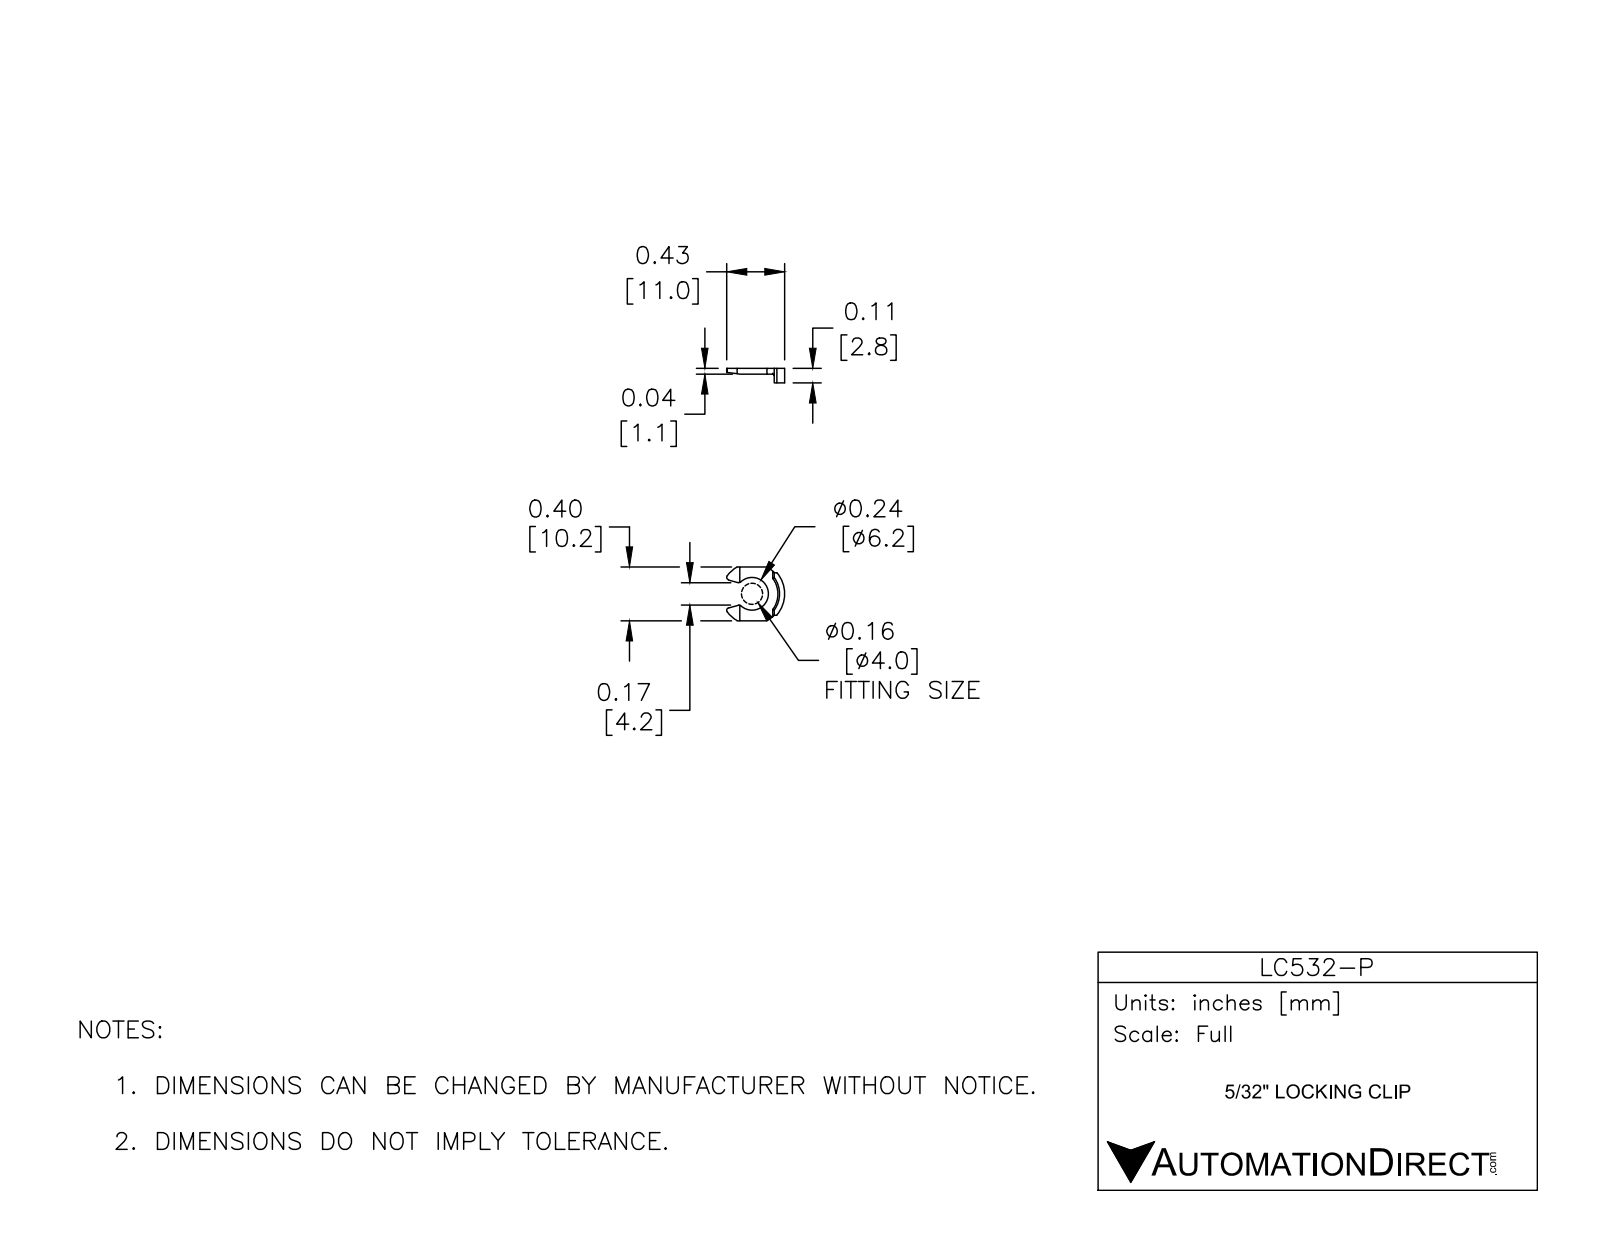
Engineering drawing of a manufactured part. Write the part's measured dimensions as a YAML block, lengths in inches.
part_name: "LC532-P"
step_written_by: "SolidWorks 2017 (AUTOMOTIVE_DESIGN)"
units: inches
bodies: {solids: 1, faces: 30, planar: 13, cylindrical: 16, other: 1}
overall_size: [0.434, 0.402, 0.11]
volume: 0.005
surface_area: 0.316
partial_cylinders:
  - {radius: 0.02, count: 4}
  - {radius: 0.012, count: 1}
  - {radius: 0.122, count: 1}
  - {radius: 0.205, count: 1}
  - {radius: 0.229, count: 1}
  - {radius: 0.244, count: 1}
face_to_face_distances: [0.043, 0.11, 0.067, 0.402, 0.042, 0.359, 0.317]
